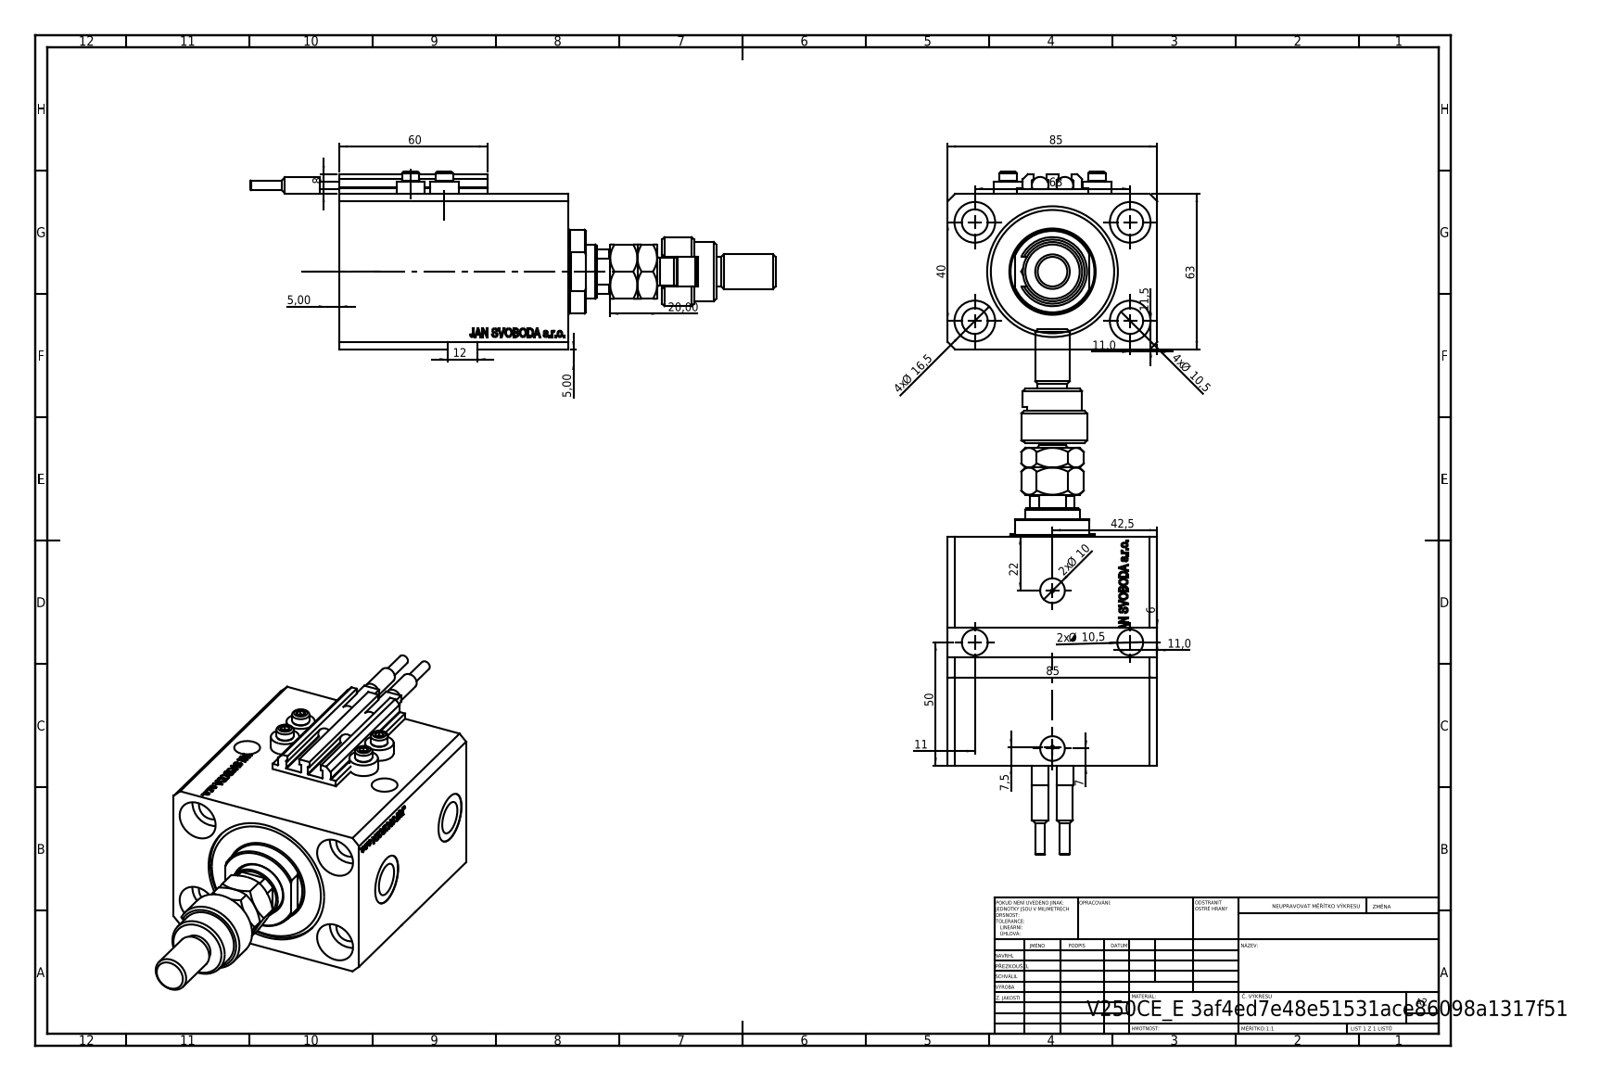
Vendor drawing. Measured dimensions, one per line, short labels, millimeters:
name: FEMALE_PART_FOR_DFA; SWITCH_V250CE; V250CE_C_VCP; V250CE_E_Body (+3 more)
written by: SolidWorks 2019 (CONFIG_CONTROL_DESIGN)
unit: mm
bodies: 12 solids, 1224 faces (595 planar, 151 cylindrical, 478 other)
size: 212.9 × 85 × 72
volume: 462 718 mm³; area: 108 661 mm²
holes: 6× ⌀10.5, 4× ⌀1.25, 4× ⌀4, 4× ⌀16.5, 2× ⌀10, 2× ⌀13.16, 2× ⌀20, 1× ⌀12.5, 1× ⌀22, 1× ⌀40, 1× ⌀53
bosses: 4× ⌀11.6, 4× ⌀7, 2× ⌀6.8, 2× ⌀6.5, 2× ⌀4, 1× ⌀34, 1× ⌀28, 1× ⌀24
rounds: 10× R0.2, 1× R9.75, 1× R10.5
face distances: 63, 85, 93, 65.9, 54.5, 27.1, 3, 11.4, 81.6, 65
hole spacings: 37.31, 63, 13.6, 15.4, 24.96, 28.02, 28.43, 33.62
